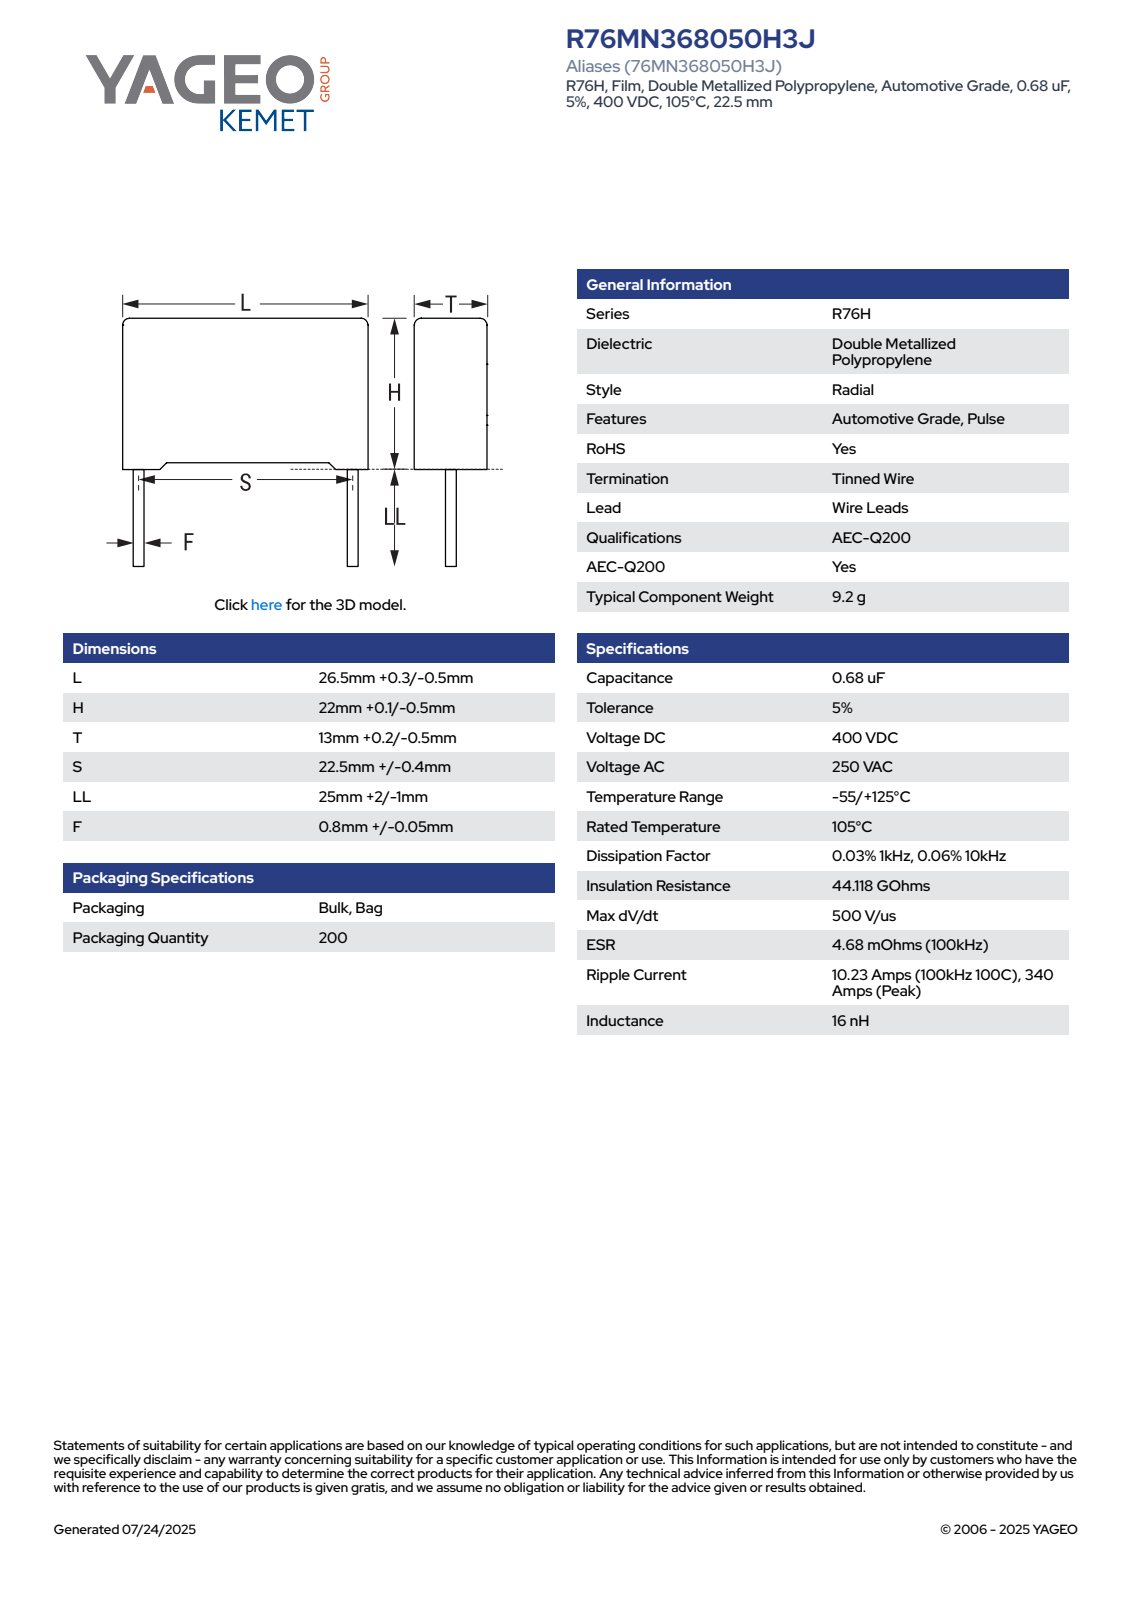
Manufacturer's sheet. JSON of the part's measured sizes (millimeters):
{"part_name": "CFR_RB2R76_26.5X22X13_L26.8H22.1T13.2S22.5LL27F0.85", "step_written_by": "SolidWorks 2014 (AUTOMOTIVE_DESIGN)", "units": "millimeters", "bodies": {"solids": 4, "faces": 85, "planar": 77, "cylindrical": 8, "other": 0}, "overall_size": [49.1, 26.8, 13.21], "volume_mm3": 7603, "surface_area_mm2": 2659, "round_bosses_or_shafts": [[0.85, 2]], "partial_cylinders_radius": [[0.5, 4]], "face_to_face_distances": [13.2, 26.8, 21.34, 21.35, 0.75, 0.76, 22.1, 0.89, 25.91, 13.21]}
